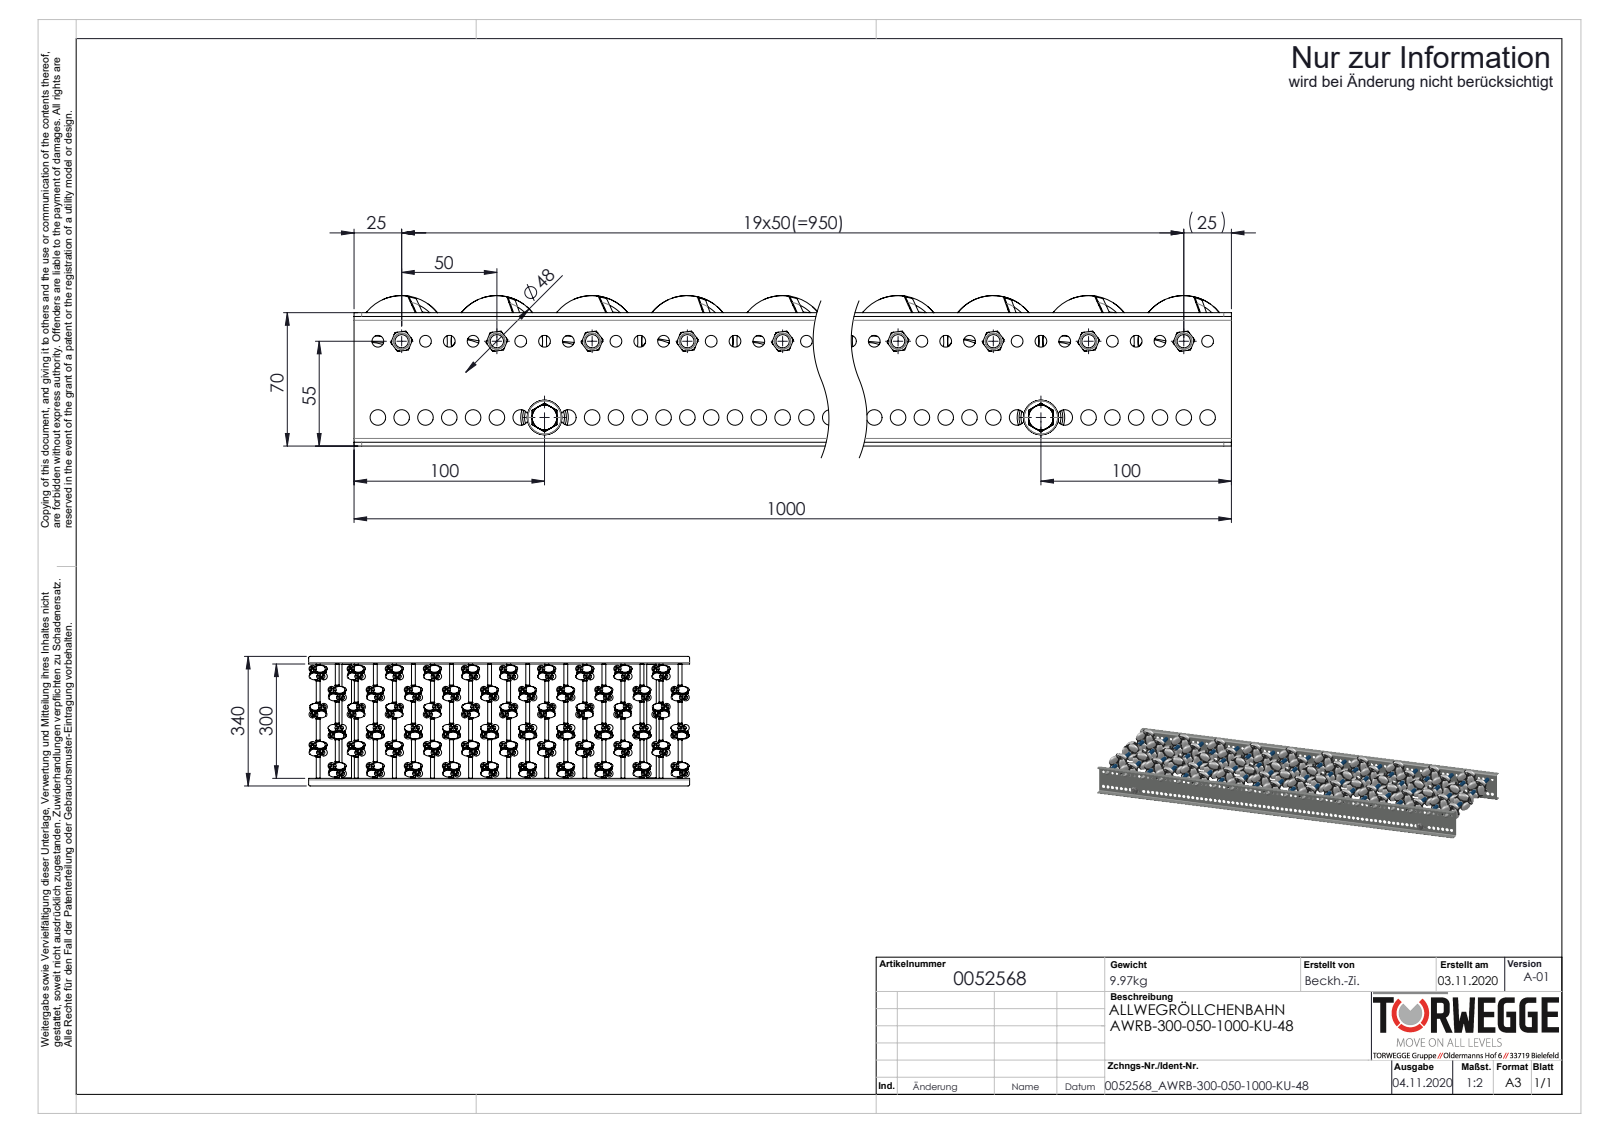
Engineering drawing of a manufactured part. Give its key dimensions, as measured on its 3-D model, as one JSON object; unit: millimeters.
{"part_name": "0015028_AWR48; Traversen_KFG_L300; 0036819_SICHERUNGS-HUTMUTTER-DIN986-M6; S100994_Sperrzahnschraube_M08x16-8.8-A2K (+8 more)", "step_written_by": "SolidWorks 2020 (AUTOMOTIVE_DESIGN)", "units": "millimeters", "bodies": {"solids": 1032, "faces": 18552, "planar": 6360, "cylindrical": 7128, "other": 5064}, "overall_size": [1000, 340, 78.99], "volume_mm3": 3400000, "surface_area_mm2": 2338000, "round_holes": [[3.7, 360], [4.2, 360], [6.2, 79], [8.2, 79], [4.92, 20], [6.5, 20], [8.4, 20], [6.8, 2], [21, 2]], "round_bosses_or_shafts": [[4, 360], [3.7, 306], [8, 22], [42, 20], [11, 20], [10, 20], [7, 20], [6, 20]], "partial_cylinders_radius": [[23.55, 20], [4, 8], [2, 4]], "face_to_face_distances": [2, 302, 68, 300, 304, 70, 66, 5, 55.2, 20], "hole_center_spacings": [36.06, 36.05, 100, 50, 36.07, 36.04, 200, 150]}
